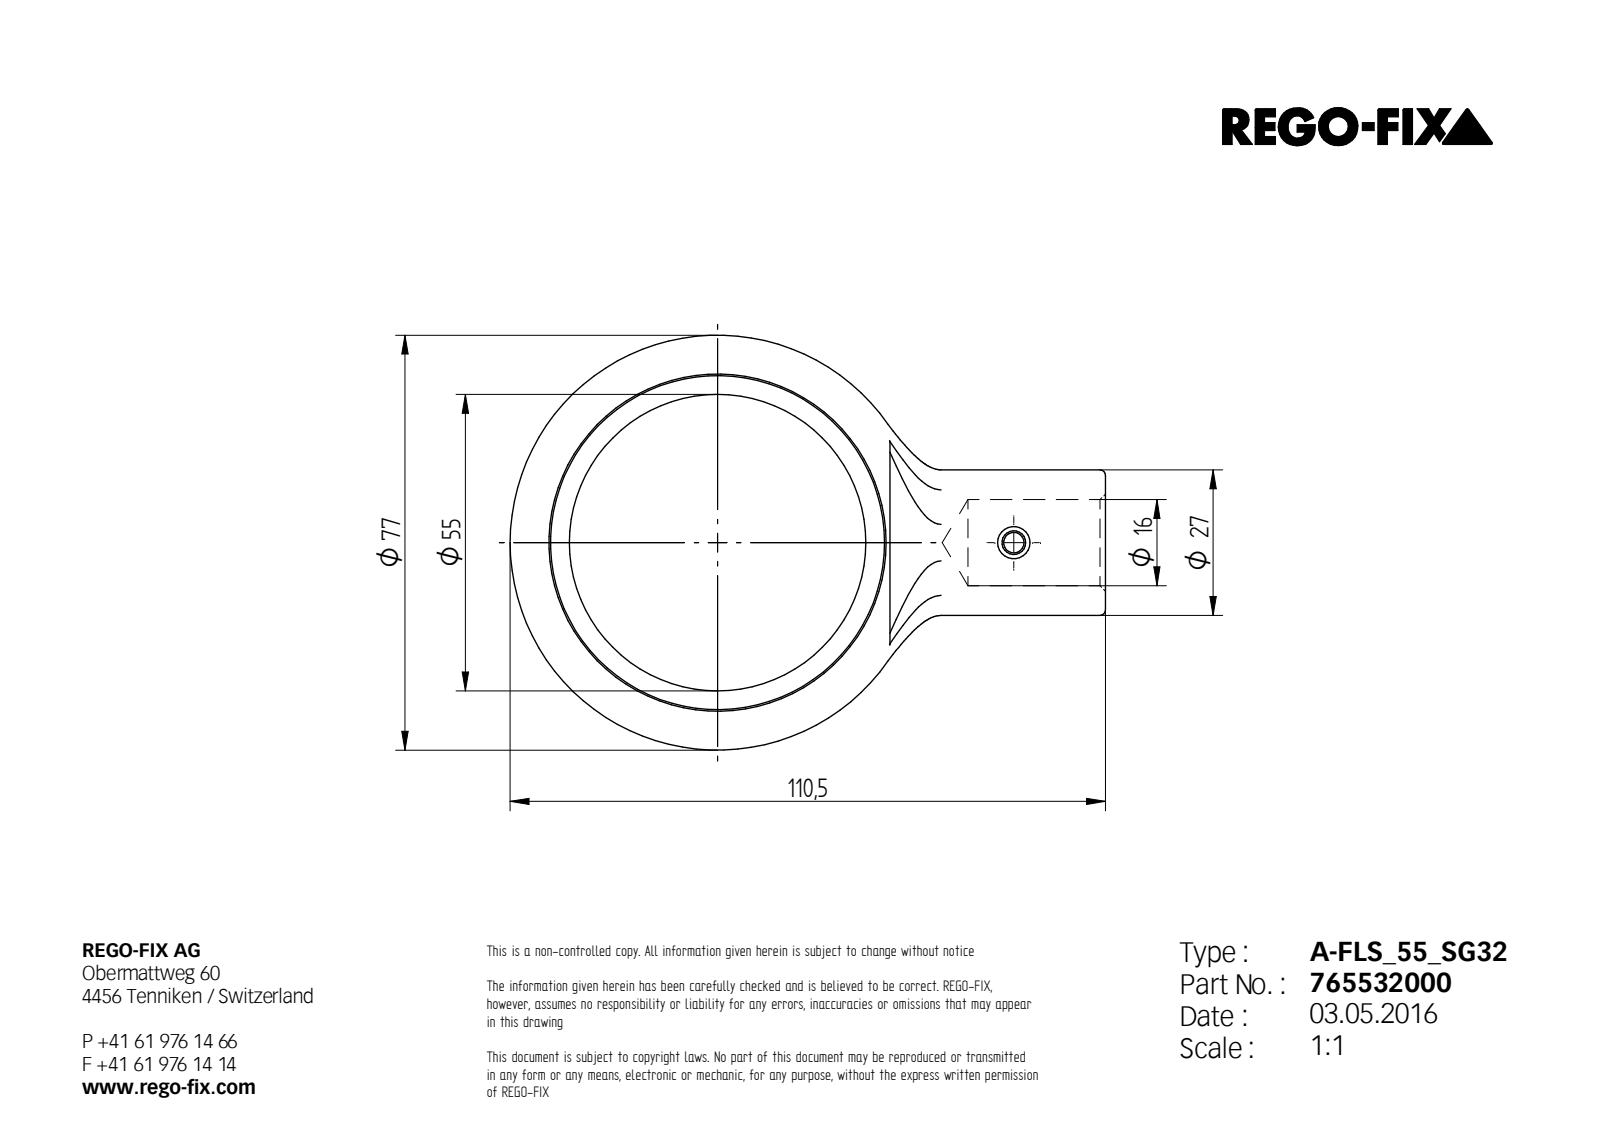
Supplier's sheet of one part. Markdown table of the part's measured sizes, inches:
| quantity | value |
| --- | --- |
| part name | 0005712; 0006879; 0006880; 0005710 |
| STEP written by | Unknown (AUTOMOTIVE_DESIGN) |
| units | inches |
| bodies | 4 solids, 123 faces (70 planar, 15 cylindrical, 38 other) |
| overall size | 4.35 × 3.031 × 1.161 |
| volume | 4.17 in³ |
| surface area | 43.43 in² |
| round holes (diameter × count) | 0.177 × 1, 0.217 × 1, 0.63 × 1, 2.165 × 1, 2.441 × 1 |
| round bosses / shafts (diameter × count) | 1.063 × 1, 0.205 × 1, 0.173 × 1, 0.138 × 1 |
| partial cylindrical surfaces (radius × count) | 0.157 × 1, 1.136 × 1, 1.148 × 1 |
| main face-to-face distances | 0.984, 0.138, 1.122, 0.039, 0.098, 1.118, 0.98, 0.059, 1.02, 1.024 |
| hole center spacings | 2.165 |
